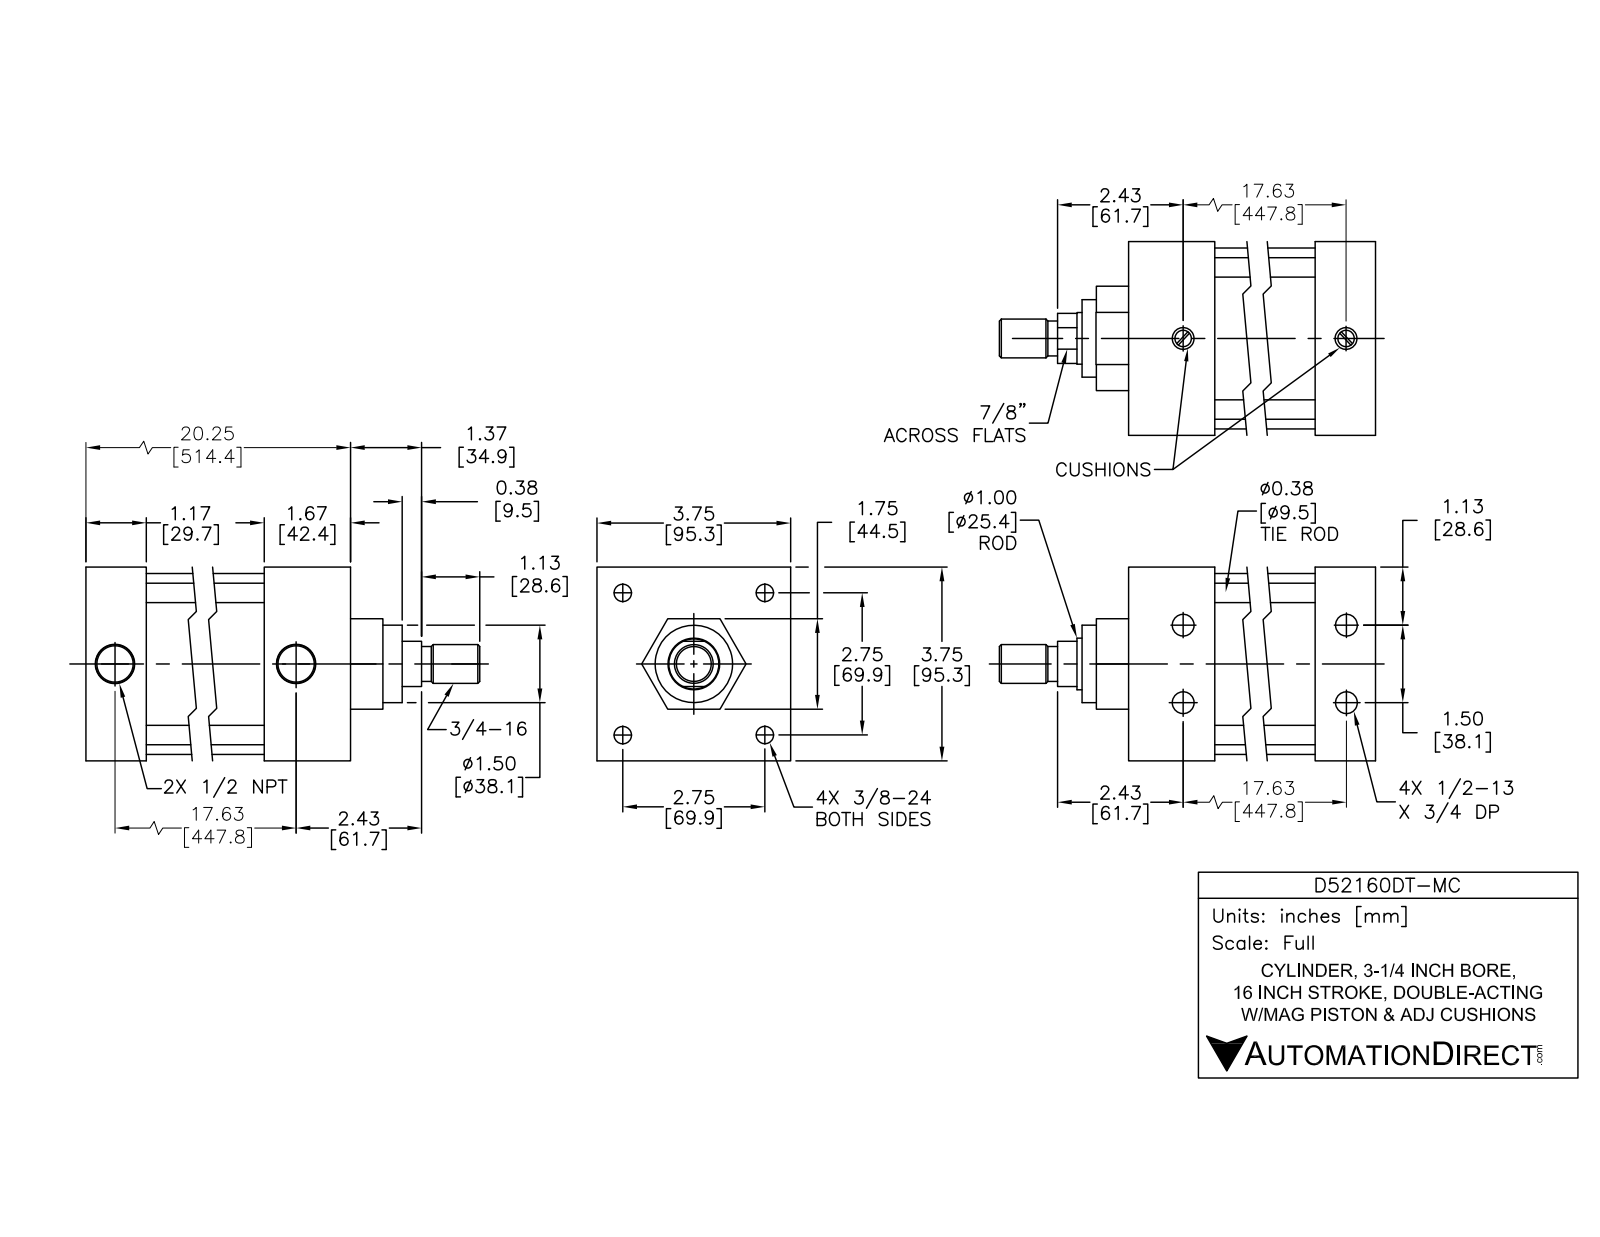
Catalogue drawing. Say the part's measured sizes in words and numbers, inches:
The part is named "D52160DT-MC; D52160DT-M PISTON; D52160DT-M BODY". Its 3-D file was written by "SolidWorks 2015 (AUTOMOTIVE_DESIGN)". It is 12 solids with 303 faces: 99 planar, 114 cylindrical and 90 other. Overall it measures 22.745 by 3.75 by 3.75 inches. Its volume is 93.34 cubic inches and its surface area 694.8 square inches. Round holes: 4 of diameter 0.33, 4 of diameter 0.406, 4 of diameter 0.417, 4 of diameter 0.625, 2 of diameter 0.5, 2 of diameter 0.766, 1 of diameter 1, 1 of diameter 1.003, 1 of diameter 3.25. Round bosses or shafts: 4 of diameter 0.609, 4 of diameter 0.375, 4 of diameter 0.34, 1 of diameter 3.5, 1 of diameter 3.247, 1 of diameter 1.75, 1 of diameter 0.997, 1 of diameter 0.97. Partial cylindrical surfaces (rounded edges, fillets, slot ends): 4 of radius 0.375. The main face-to-face distances are 3.75, 0.08, 17.326, 20.246, 1.75, 18.997, 1.249, 17.751, 1.246, 2.495. The hole center spacings are 0.75, 0.76, 1.5, 1.95, 1.95, 2.758, 2.758, 3.9.
